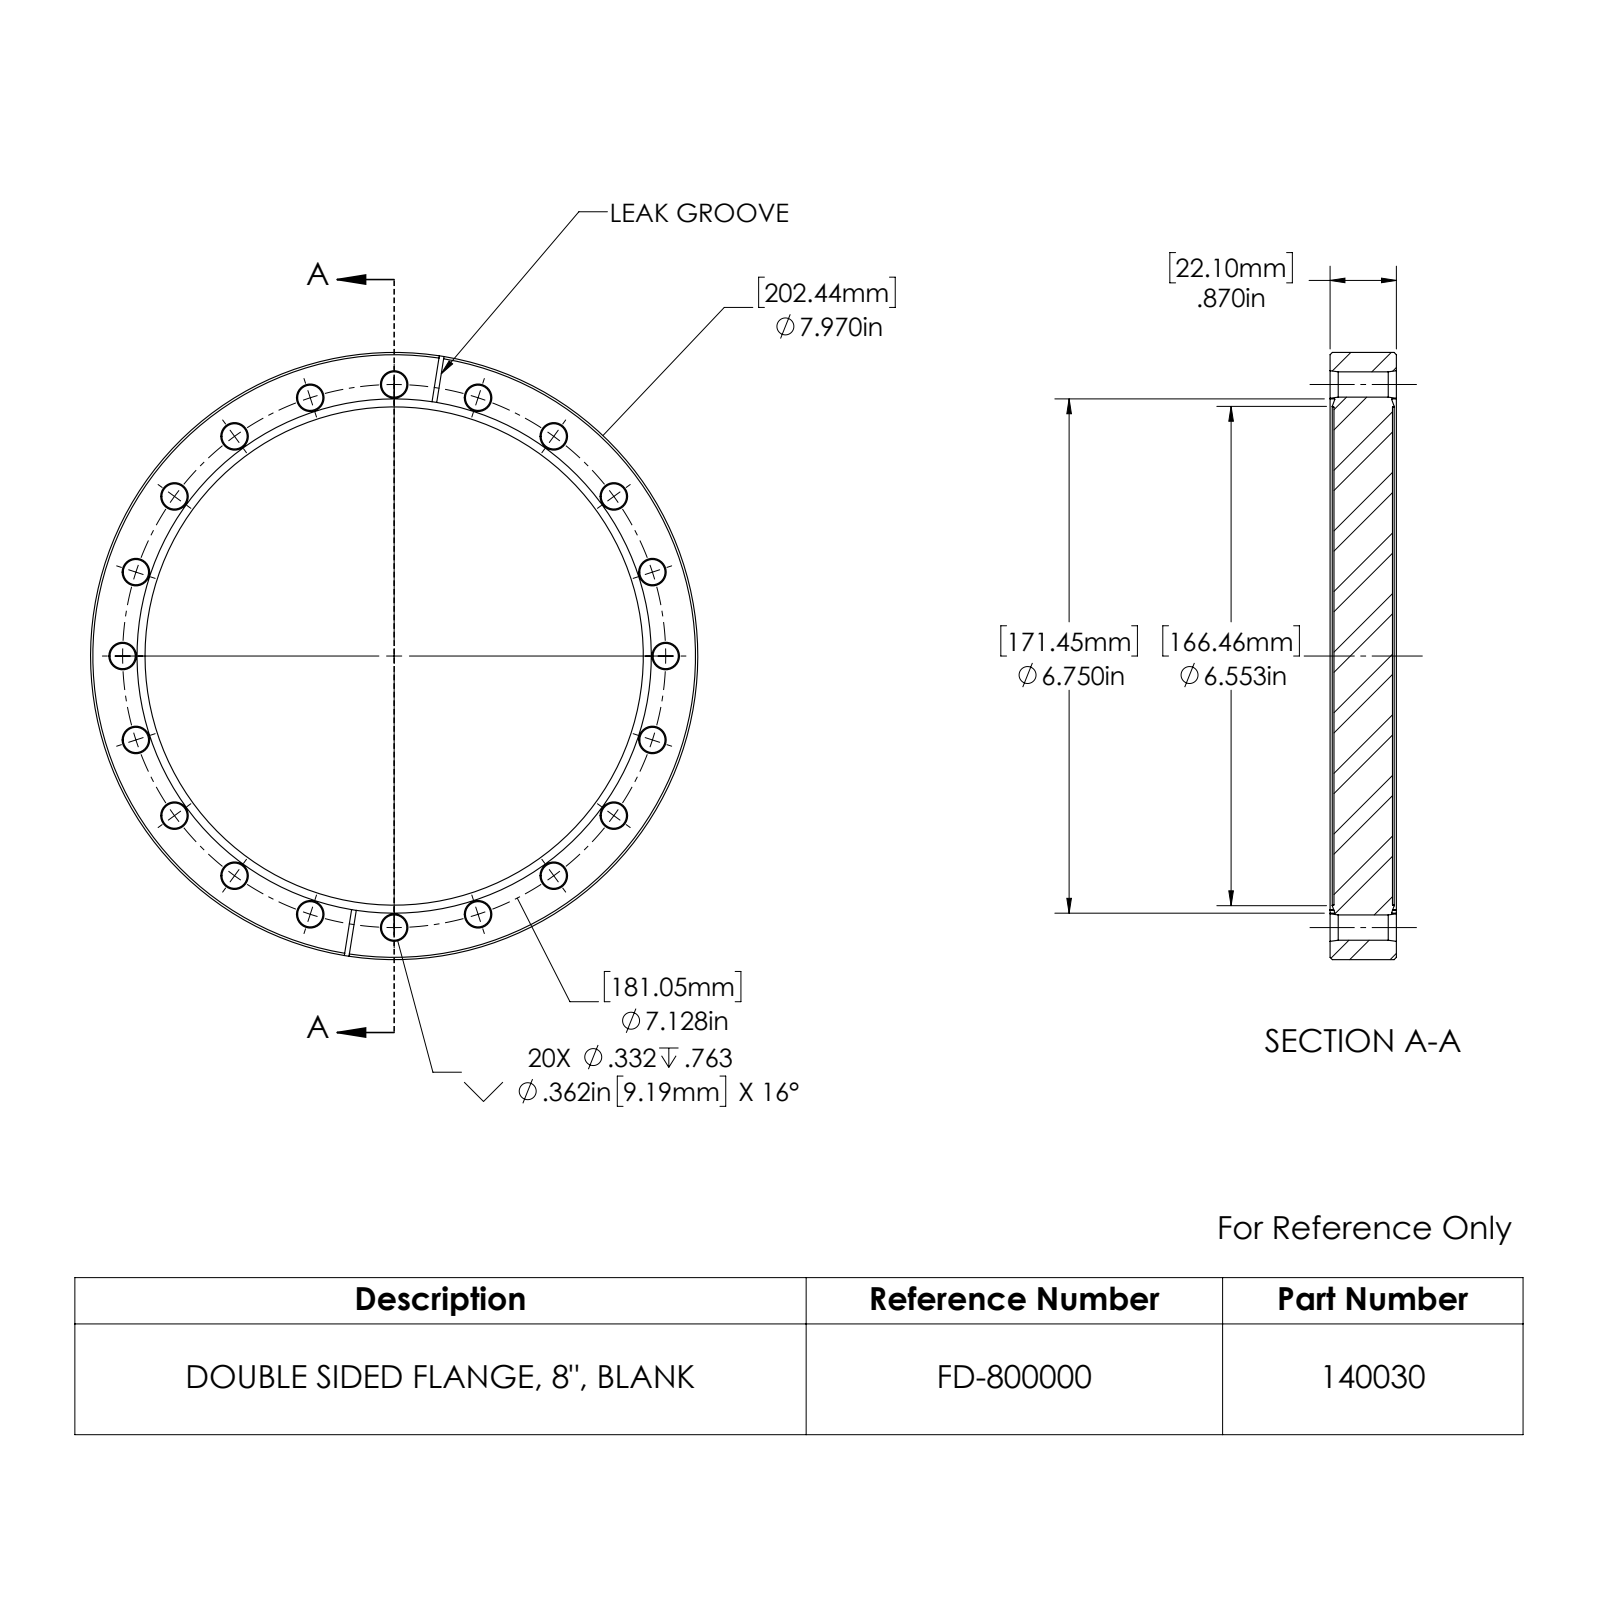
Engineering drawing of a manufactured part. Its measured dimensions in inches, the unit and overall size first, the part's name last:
Units: inches
Overall size (bounding box): 7.97 × 7.97 × 0.87
Round holes (diameter × count): ⌀0.332 ×20, ⌀6.54 ×1, ⌀6.75 ×1
Round bosses / shafts (diameter × count): ⌀7.97 ×1
Partial cylindrical surfaces — rounded edges, fillets, slot ends (radius × count): R1.25 ×4
Main face-to-face distances: 0.768, 0.051, 0.819, 0.87, 0.062, 0.065, 0.058
Hole centre spacings: 4.19, 1.115, 2.203, 5.767, 6.351, 7.04, 3.236, 3.564
Volume: 38.2 in³ · Surface area: 139.1 in²
Bodies: 1 solid, 170 faces (14 planar, 54 cylindrical, 102 other)
Part name (STEP PRODUCT): 140030_A
STEP written by: SolidWorks 2022 (CONFIG_CONTROL_DESIGN)
